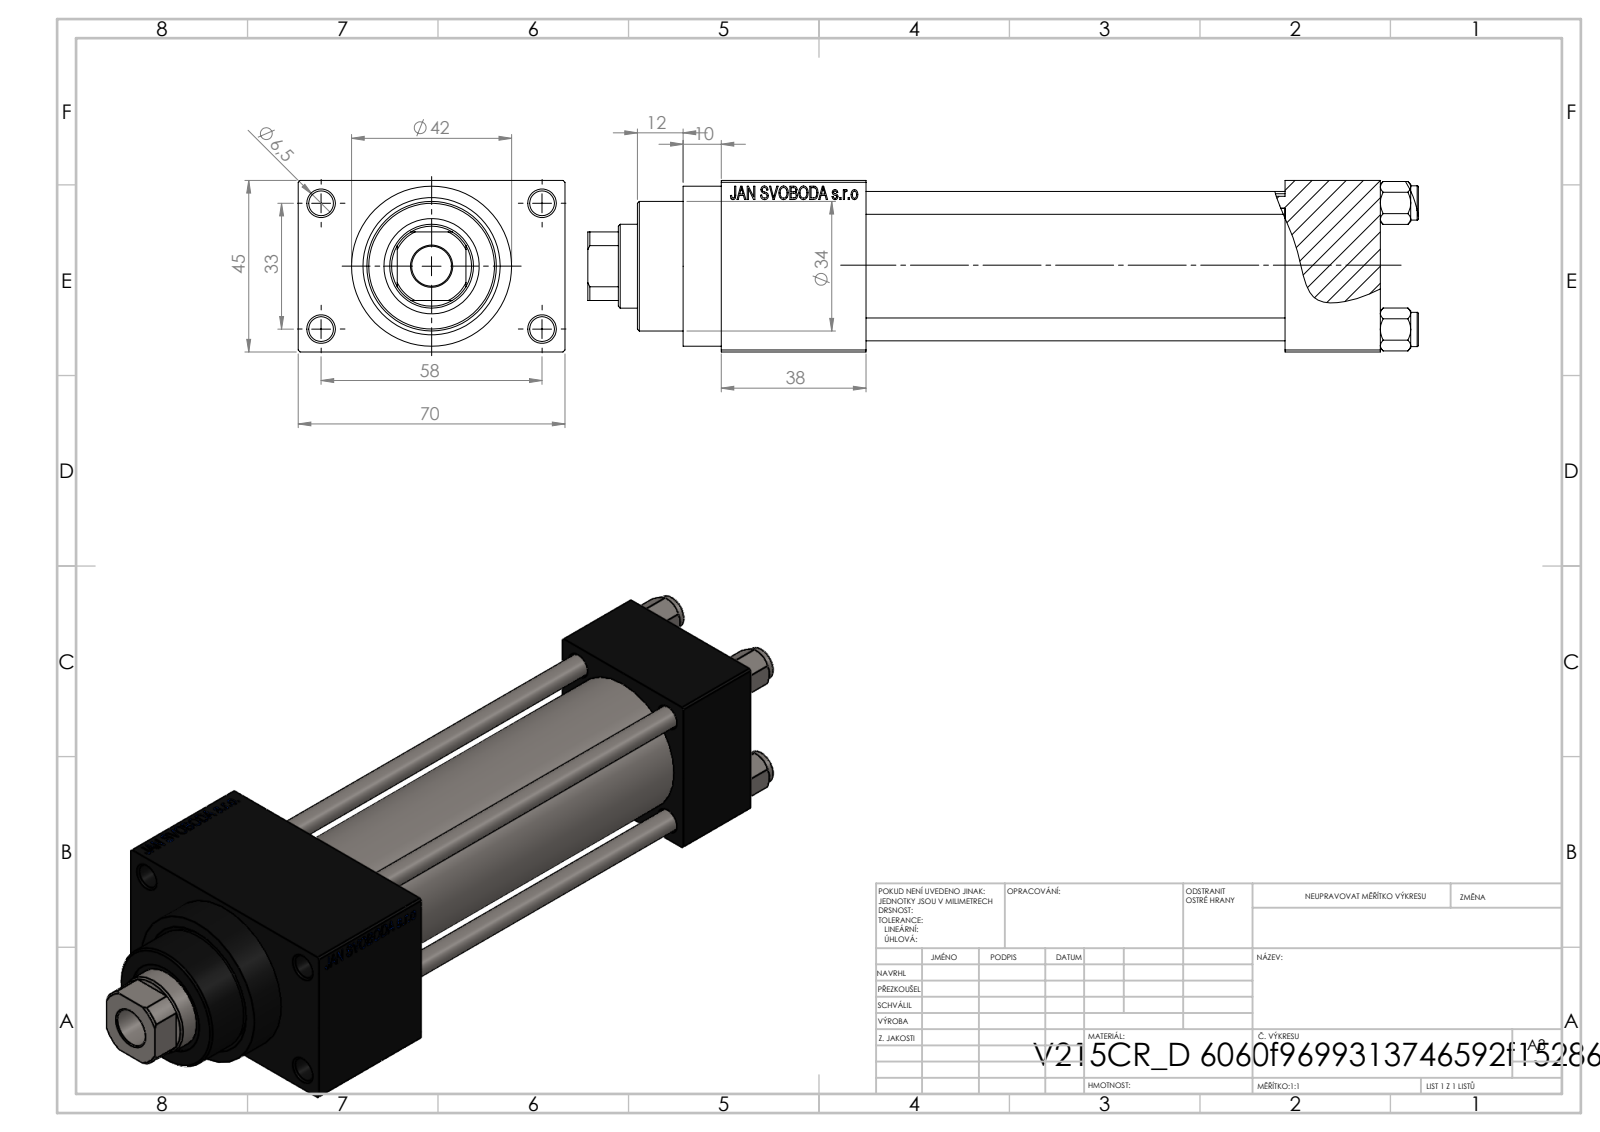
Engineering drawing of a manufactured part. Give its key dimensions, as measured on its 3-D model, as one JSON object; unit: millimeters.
{"part_name": "NUT_M5_D; V215_VC_A; V215CR_D_Body; V215CR_D_TYCINKA (+1 more)", "step_written_by": "SolidWorks 2019 (CONFIG_CONTROL_DESIGN)", "units": "millimeters", "bodies": {"solids": 11, "faces": 1104, "planar": 496, "cylindrical": 88, "other": 520}, "overall_size": [218, 70, 45], "volume_mm3": 292262, "surface_area_mm2": 101749, "round_holes": [[6, 4], [6.5, 4], [7, 2], [13.16, 2], [20, 2], [10.5, 1], [22, 1], [24, 1], [25, 1], [32, 1], [33, 1]], "round_bosses_or_shafts": [[9, 4], [42, 1], [38, 1], [34, 1]], "partial_cylinders_radius": [[10.5, 1]], "face_to_face_distances": [45, 25, 12.5, 110, 135, 57.5, 148, 38, 173, 70], "hole_center_spacings": [12.4, 23.48, 33.2, 33.37, 35.35, 45.6, 56.35, 33]}
